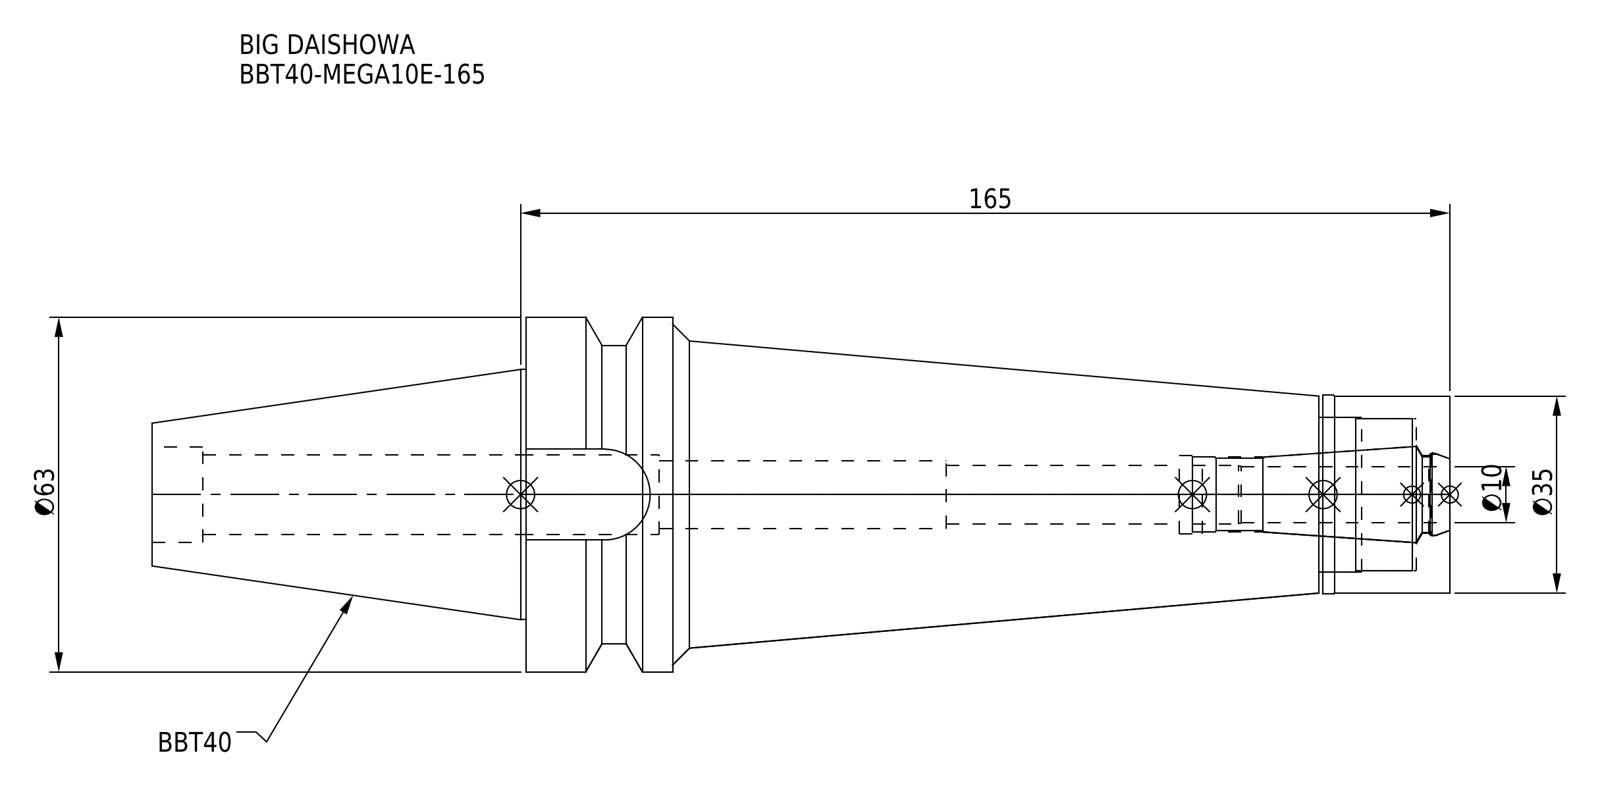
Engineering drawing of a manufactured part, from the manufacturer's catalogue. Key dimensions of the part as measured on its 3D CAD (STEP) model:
Part name (STEP PRODUCT): DXF_TEMP_ASSY_ASM_4_ASM.stp; BBT40ME10165-100_ASM.stp; BBT40-MEGA10E-165-100.stp; BBT40-MEGA10E-165-100-FreeParts (+3 more)
STEP written by: SolidWorks 2019 (CONFIG_CONTROL_DESIGN)
Units: millimetres
Bodies: 2 solids, 81 faces (21 planar, 40 cylindrical, 20 other)
Overall size (bounding box): 230.4 × 63 × 63
Volume: 311 754 mm³ · Surface area: 49 681 mm²
Round holes (diameter × count): ⌀10.4 ×1, ⌀12 ×1, ⌀13.3 ×1, ⌀13.8 ×1, ⌀13.9 ×1, ⌀14.2 ×1, ⌀14.7 ×1, ⌀17 ×1, ⌀27 ×1, ⌀27.5 ×1
Round bosses / shafts (diameter × count): ⌀63 ×1, ⌀53 ×1, ⌀44.45 ×1, ⌀35.3 ×1, ⌀35 ×1
Partial cylindrical surfaces — rounded edges, fillets, slot ends (radius × count): R8.05 ×1
Main face-to-face distances: 164, 22.5, 141.5, 23.3, 0.8, 140.7, 6.7, 15.8, 16.6, 157.3
